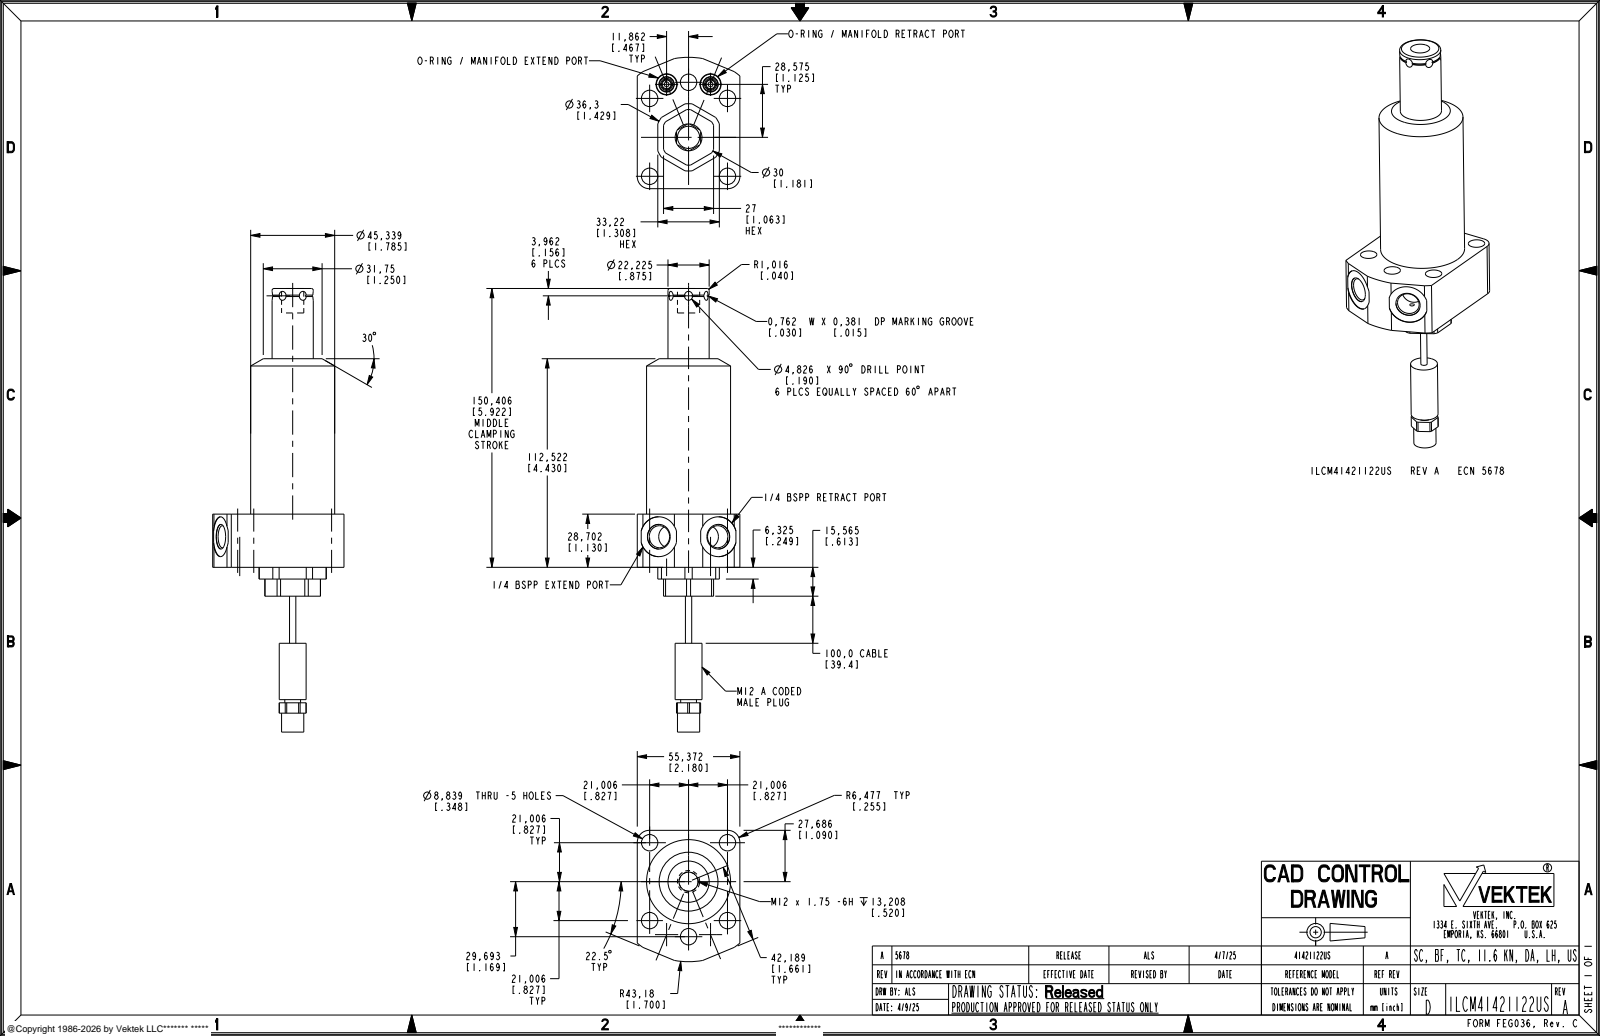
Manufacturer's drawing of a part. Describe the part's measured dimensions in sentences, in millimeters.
The part is named "ILCM41421122US". Its 3-D file was written by "CREO PARAMETRIC BY PTC INC, 2021164 (AUTOMOTIVE_DESIGN)". It is 1 solid with 198 faces: 79 planar, 85 cylindrical and 34 other. Overall it measures 239.28 by 86.87 by 63.37 millimeters. Its volume is 259 680 cubic millimeters and its surface area 38 873 square millimeters. Round holes: 5 of diameter 8.84, 2 of diameter 2.49, 2 of diameter 6.5, 2 of diameter 11.4, 2 of diameter 11.89, 2 of diameter 13.31, 2 of diameter 21.5, 1 of diameter 10.31. Round bosses or shafts: 2 of diameter 5.49, 1 of diameter 45.34, 1 of diameter 22.23, 1 of diameter 14.5, 1 of diameter 11.99, 1 of diameter 11.99, 1 of diameter 8.51, 1 of diameter 3.4. Partial cylindrical surfaces (rounded edges, fillets, slot ends): 2 of radius 6.48, 1 of radius 10.73, 1 of radius 15, 1 of radius 18.15, 1 of radius 43.18. The main face-to-face distances are 28.7, 55.38, 15.57, 44.27, 3.11, 30.11, 128.09, 112.52, 83.82, 27. The hole center spacings are 29.71, 42.02, 11.87, 11.91, 22.73, 30.93, 33.73, 50.42.
